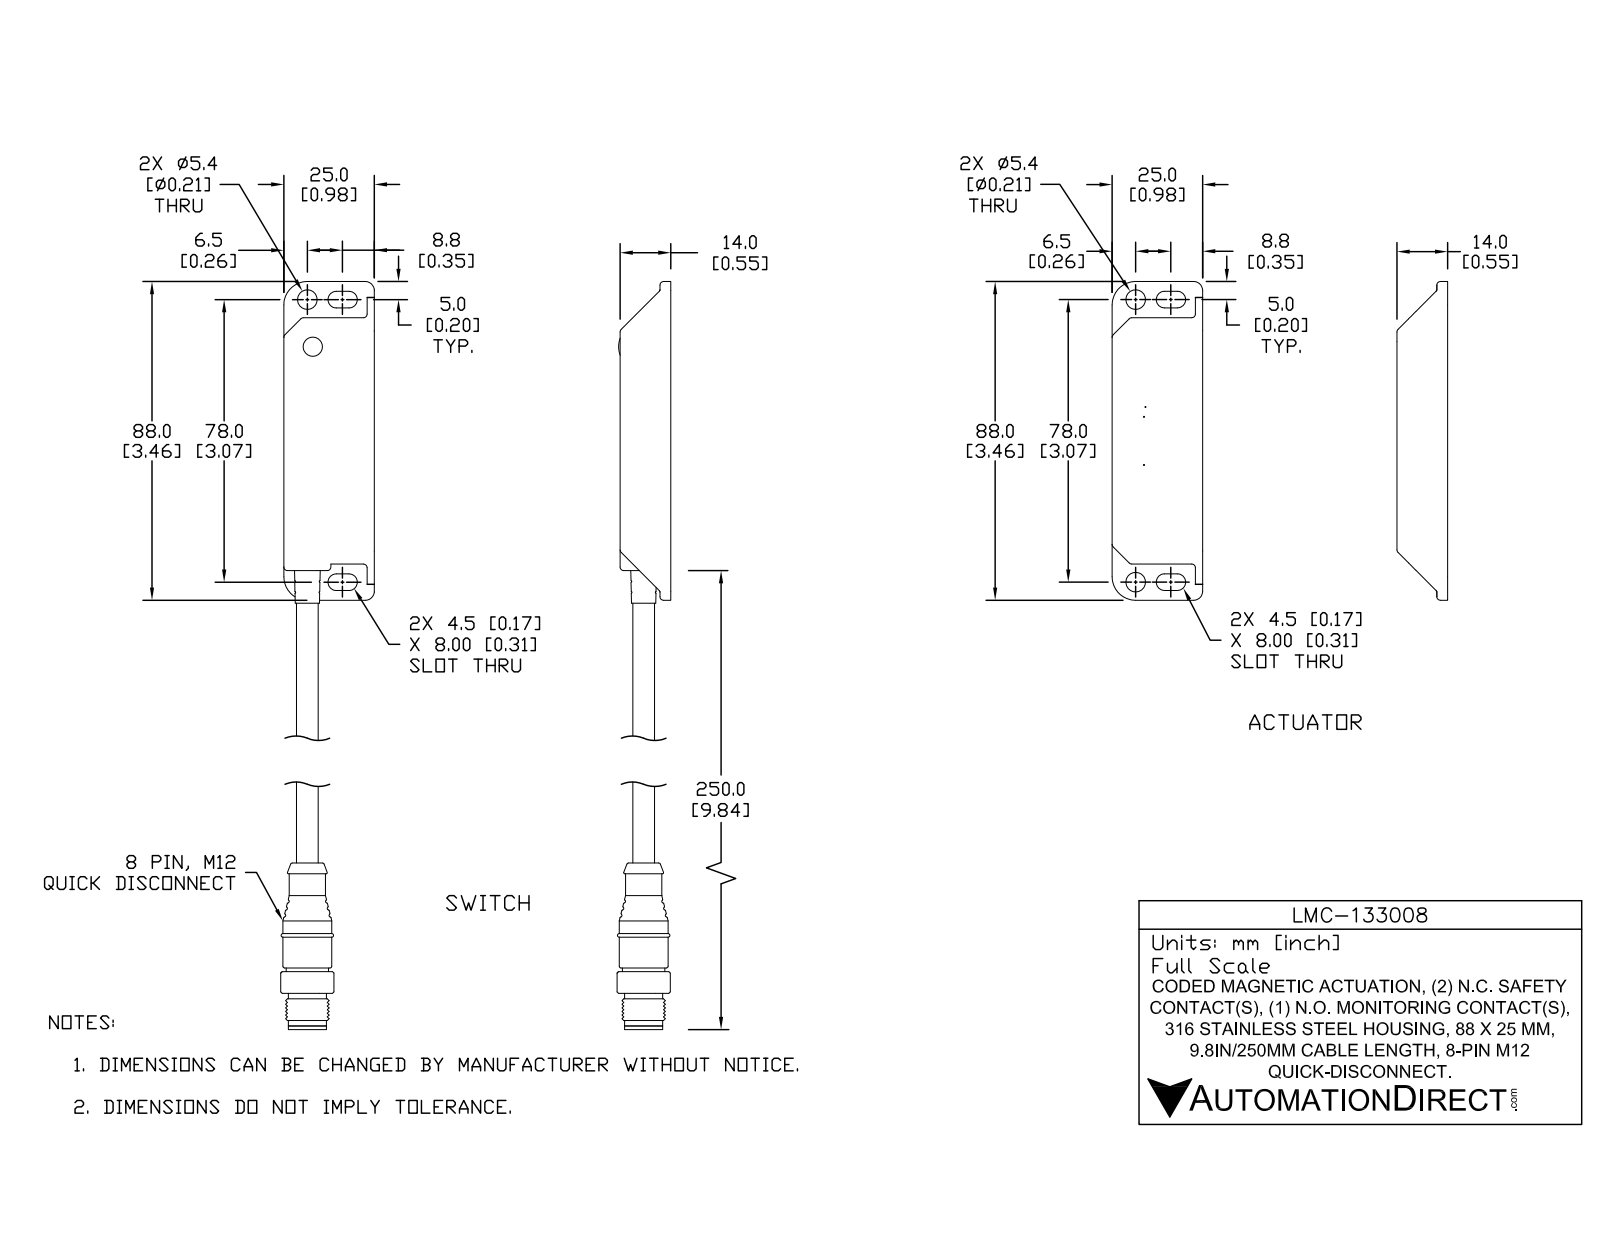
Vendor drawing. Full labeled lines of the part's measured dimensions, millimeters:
Part name (STEP PRODUCT): LMC-133008; LMC-133008_2; LMC-133008_1
STEP written by: SolidWorks 2017 (AUTOMOTIVE_DESIGN)
Units: millimetres
Bodies: 11 solids, 1033 faces (351 planar, 356 cylindrical, 326 other)
Overall size (bounding box): 329.8 × 51.8 × 14.9
Volume: 33 450 mm³ · Surface area: 34 660 mm²
Round holes (diameter × count): ⌀5 ×4, ⌀5.4 ×4, ⌀5.9 ×1, ⌀7.2 ×1, ⌀8.3 ×1, ⌀11.8 ×1
Round bosses / shafts (diameter × count): ⌀0.8 ×8, ⌀2 ×4, ⌀4.9 ×2, ⌀3.4 ×2, ⌀13.5 ×1, ⌀11.7 ×1, ⌀10.5 ×1, ⌀10 ×1
Partial cylindrical surfaces — rounded edges, fillets, slot ends (radius × count): R0.5 ×95, R1 ×45, R2.3 ×8, R2.5 ×4, R6.5 ×4, R4.9 ×1, R7.3 ×1
Main face-to-face distances: 1.7, 1.4, 26, 13.8, 12.1, 10.7, 12.4, 23.3, 1, 2.7
Hole centre spacings: 17, 29.8, 30, 31.6, 38, 42.8, 46.1, 48.4
